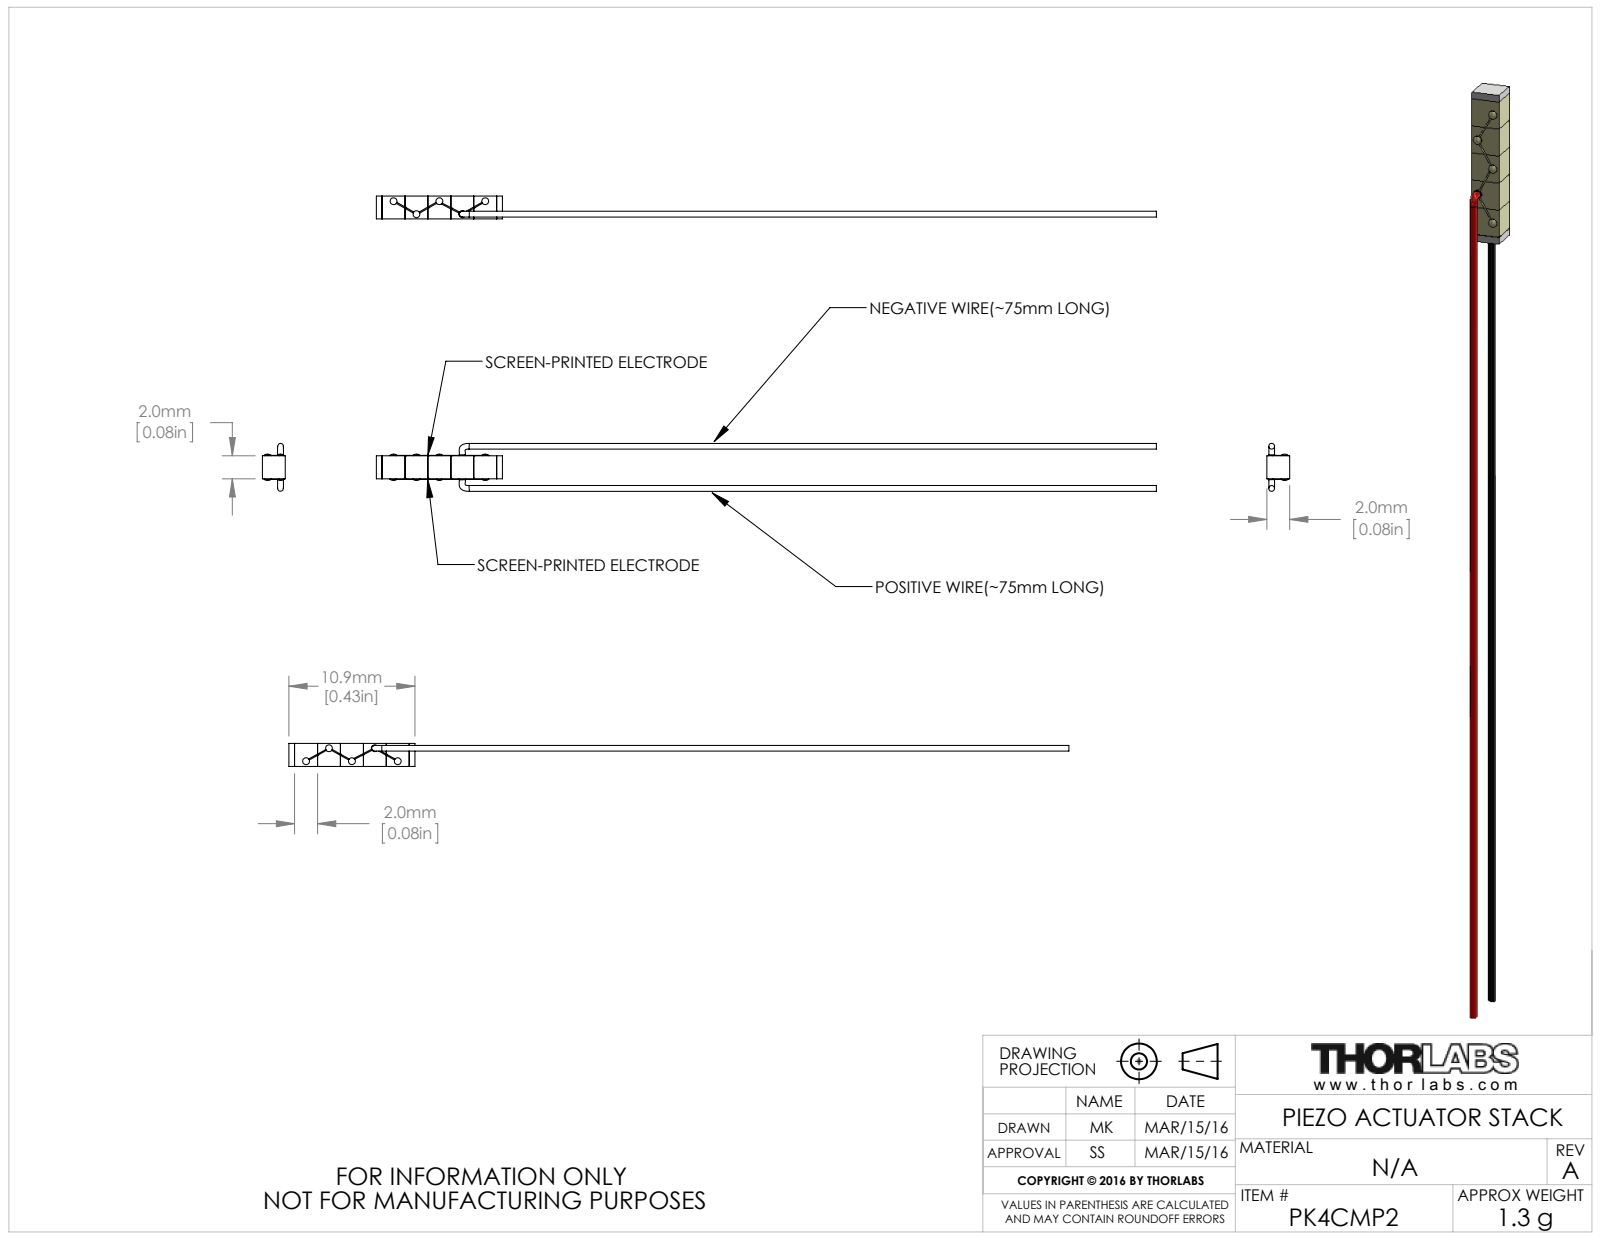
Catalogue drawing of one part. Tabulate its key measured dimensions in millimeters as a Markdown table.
| quantity | value |
| --- | --- |
| part name | CTN003603 |
| STEP written by | SolidWorks 2014 (AUTOMOTIVE_DESIGN) |
| units | millimeters |
| bodies | 3 solids, 124 faces (50 planar, 46 cylindrical, 28 other) |
| overall size | 68.1 × 4.18 × 2 |
| volume | 69 mm³ |
| surface area | 339 mm² |
| round bosses / shafts (diameter × count) | 0.6 × 5 |
| main face-to-face distances | 2, 4, 6, 8, 0.5, 10.51, 2.51, 4.51, 6.51, 8.51 |
